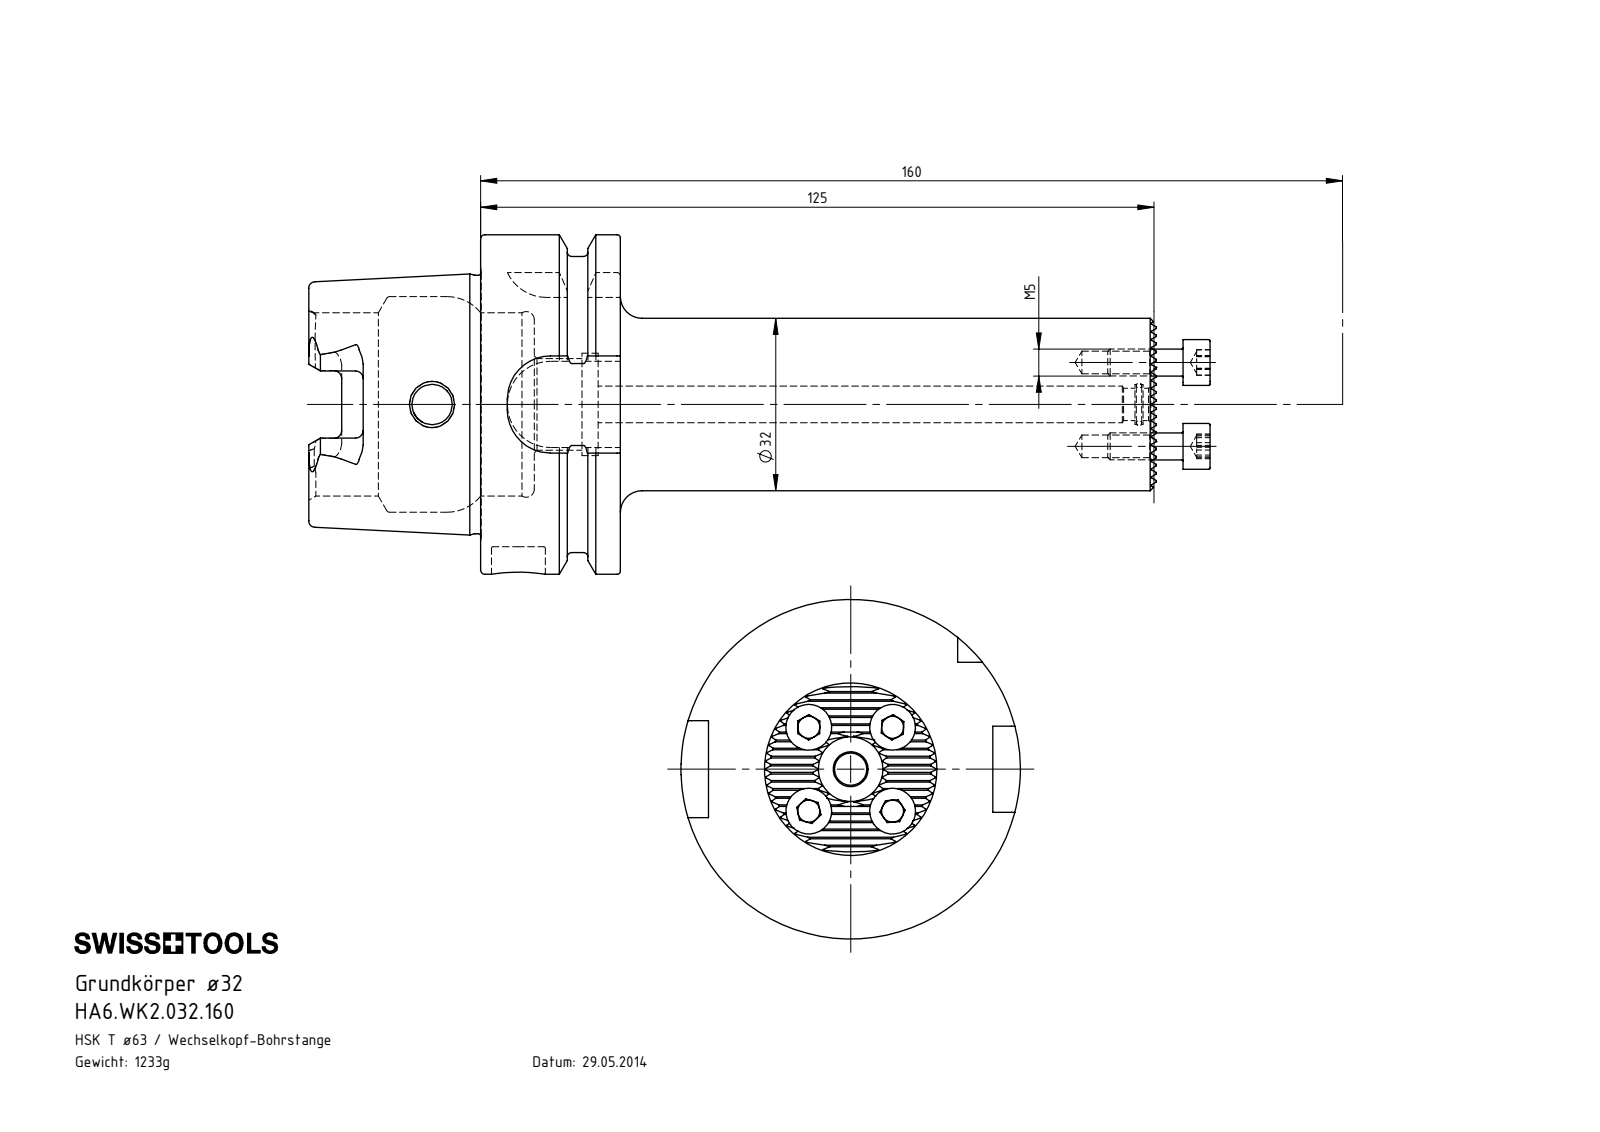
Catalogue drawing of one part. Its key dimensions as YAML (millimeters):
part_name: "ISO 4762 - M5 x 14; HA6-WK2.032.160_A; HA6.WK2.032.160; DIN 3771 - 6x1"
step_written_by: "SolidWorks 2017 (AUTOMOTIVE_DESIGN)"
units: millimeters
bodies: {solids: 5, faces: 459, planar: 223, cylindrical: 113, other: 123}
overall_size: [167.3, 63, 63]
volume: 158401
surface_area: 36675
round_holes:
  - {diameter: 4.2, count: 4}
  - {diameter: 6, count: 1}
  - {diameter: 6.8, count: 1}
  - {diameter: 7.4, count: 1}
  - {diameter: 7.5, count: 1}
  - {diameter: 10, count: 1}
  - {diameter: 17, count: 1}
  - {diameter: 19, count: 1}
  - {diameter: 34, count: 1}
  - {diameter: 40, count: 1}
round_bosses_or_shafts:
  - {diameter: 8.5, count: 3}
  - {diameter: 5, count: 3}
  - {diameter: 63, count: 1}
  - {diameter: 54.95, count: 1}
  - {diameter: 47.94, count: 1}
  - {diameter: 32, count: 1}
partial_cylinders:
  - {radius: 0.12, count: 21}
  - {radius: 1.4, count: 6}
  - {radius: 2.88, count: 4}
  - {radius: 8, count: 4}
face_to_face_distances: [25.95, 1.3, 16, 9.95, 2.6, 3.9, 5.2, 31.9, 41.85, 57.85]
hole_center_spacings: [11, 15.56, 22.01]
